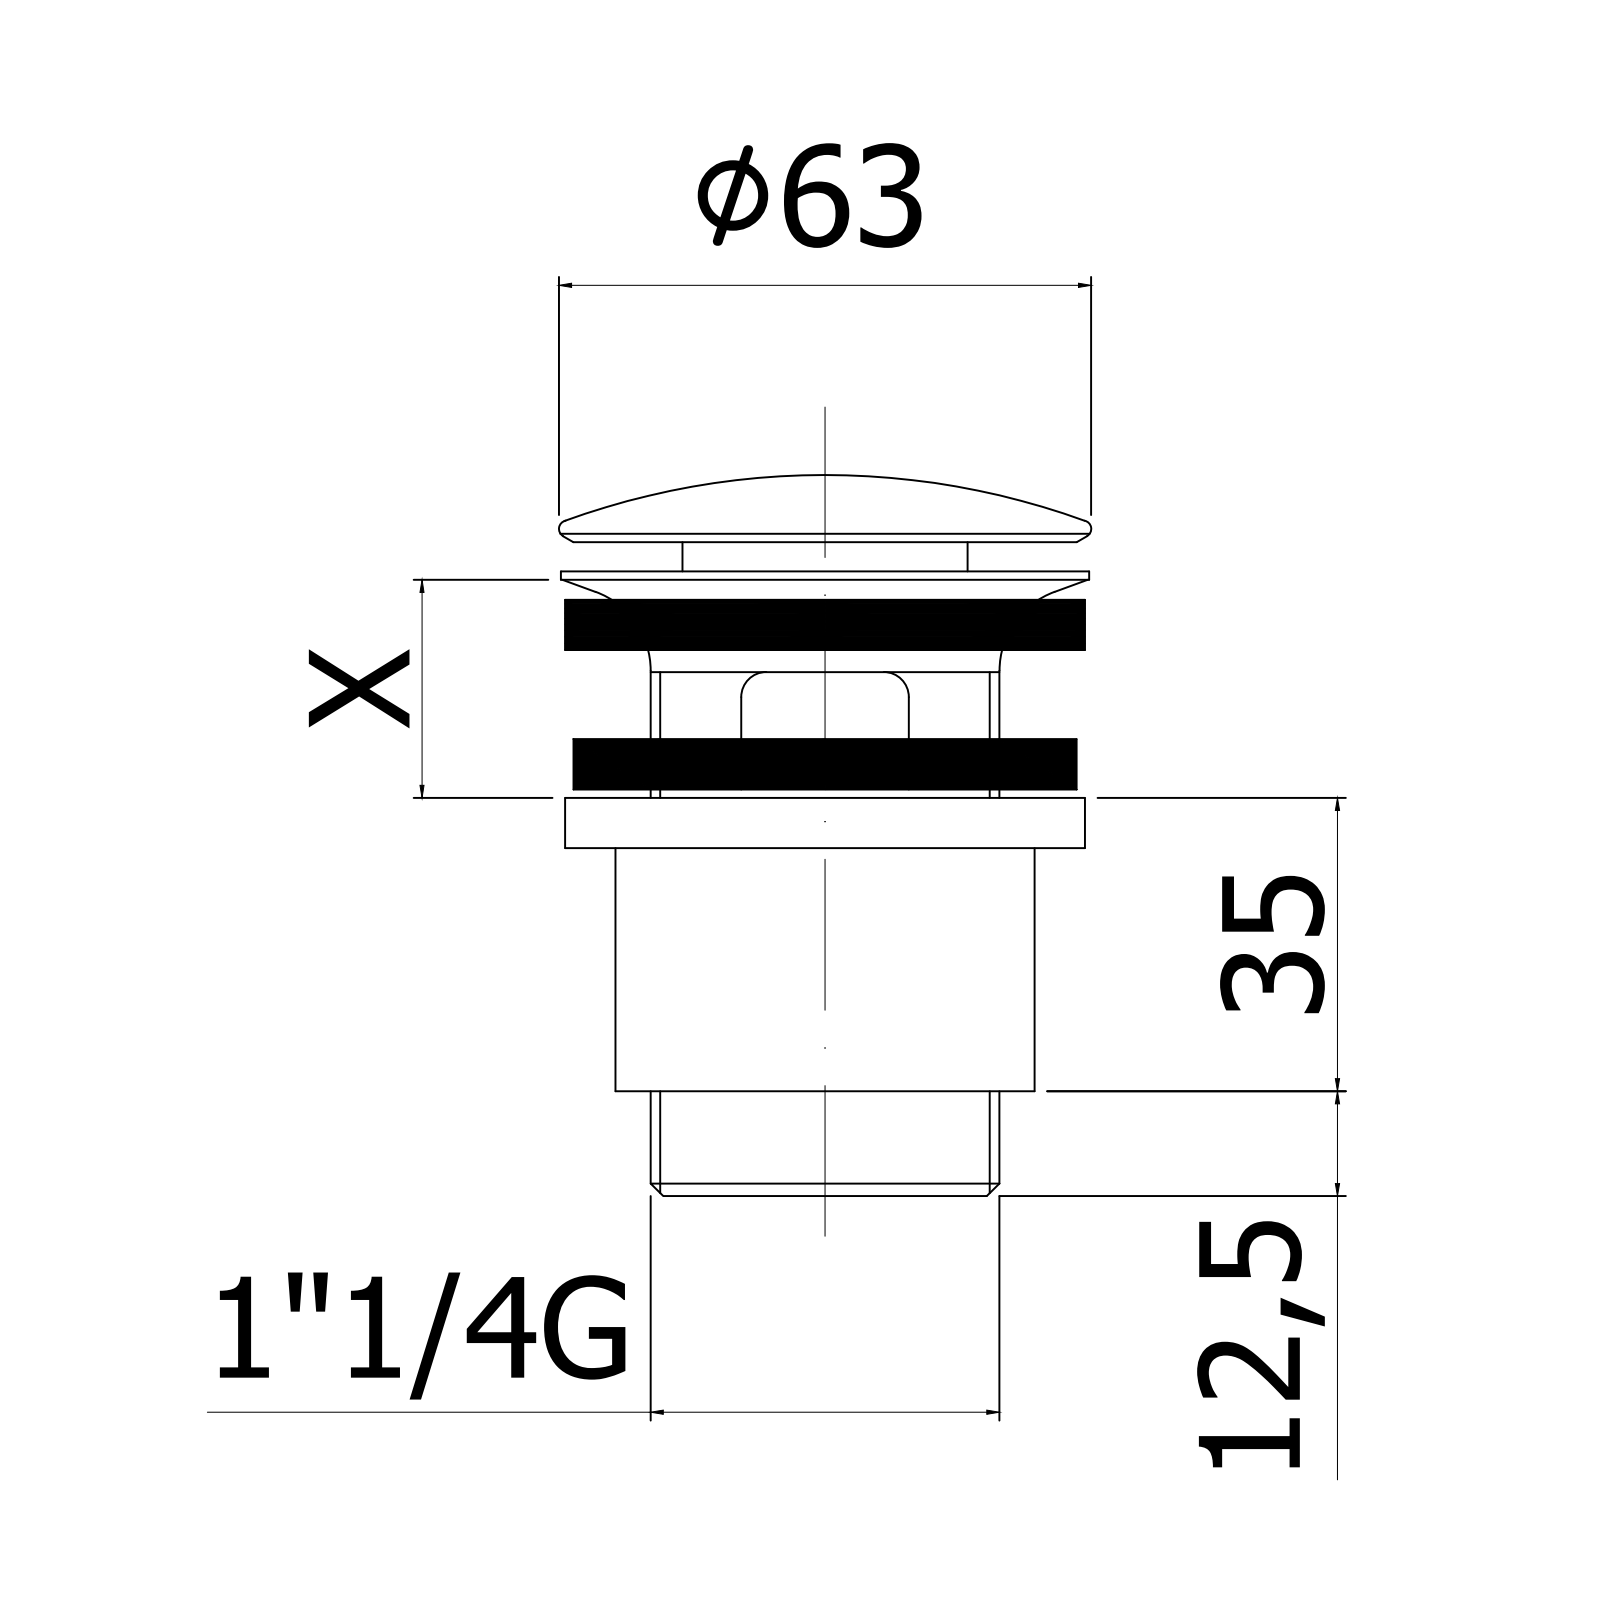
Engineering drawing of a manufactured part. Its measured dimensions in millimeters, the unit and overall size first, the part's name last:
Units: millimetres
Overall size (bounding box): 111.2 × 63 × 63
Round holes (diameter × count): ⌀11.89 ×1, ⌀15.4 ×1, ⌀17.7 ×1, ⌀22 ×1, ⌀24.3 ×1, ⌀30 ×1, ⌀30.5 ×1, ⌀32.4 ×1, ⌀33.6 ×1, ⌀35.6 ×1, ⌀37 ×1, ⌀39.27 ×1
Round bosses / shafts (diameter × count): ⌀62 ×1, ⌀61 ×1, ⌀60 ×1, ⌀49 ×1, ⌀43.4 ×1, ⌀39 ×1, ⌀34 ×1, ⌀32 ×1
Partial cylindrical surfaces — rounded edges, fillets, slot ends (radius × count): R2 ×16, R1 ×12, R0.2 ×2, R2 ×2, R4.25 ×1, R8 ×1, R8.7 ×1, R13.05 ×1
Main face-to-face distances: 38, 2, 2.25, 35.75, 11, 4.25, 40, 30, 4.5, 81
Volume: 74 532 mm³ · Surface area: 61 478 mm²
Bodies: 1 solid, 543 faces (216 planar, 175 cylindrical, 152 other)
Part name (STEP PRODUCT): ZSCA010CR
STEP written by: CREO PARAMETRIC BY PTC INC, 2020044 (CONFIG_CONTROL_DESIGN)
